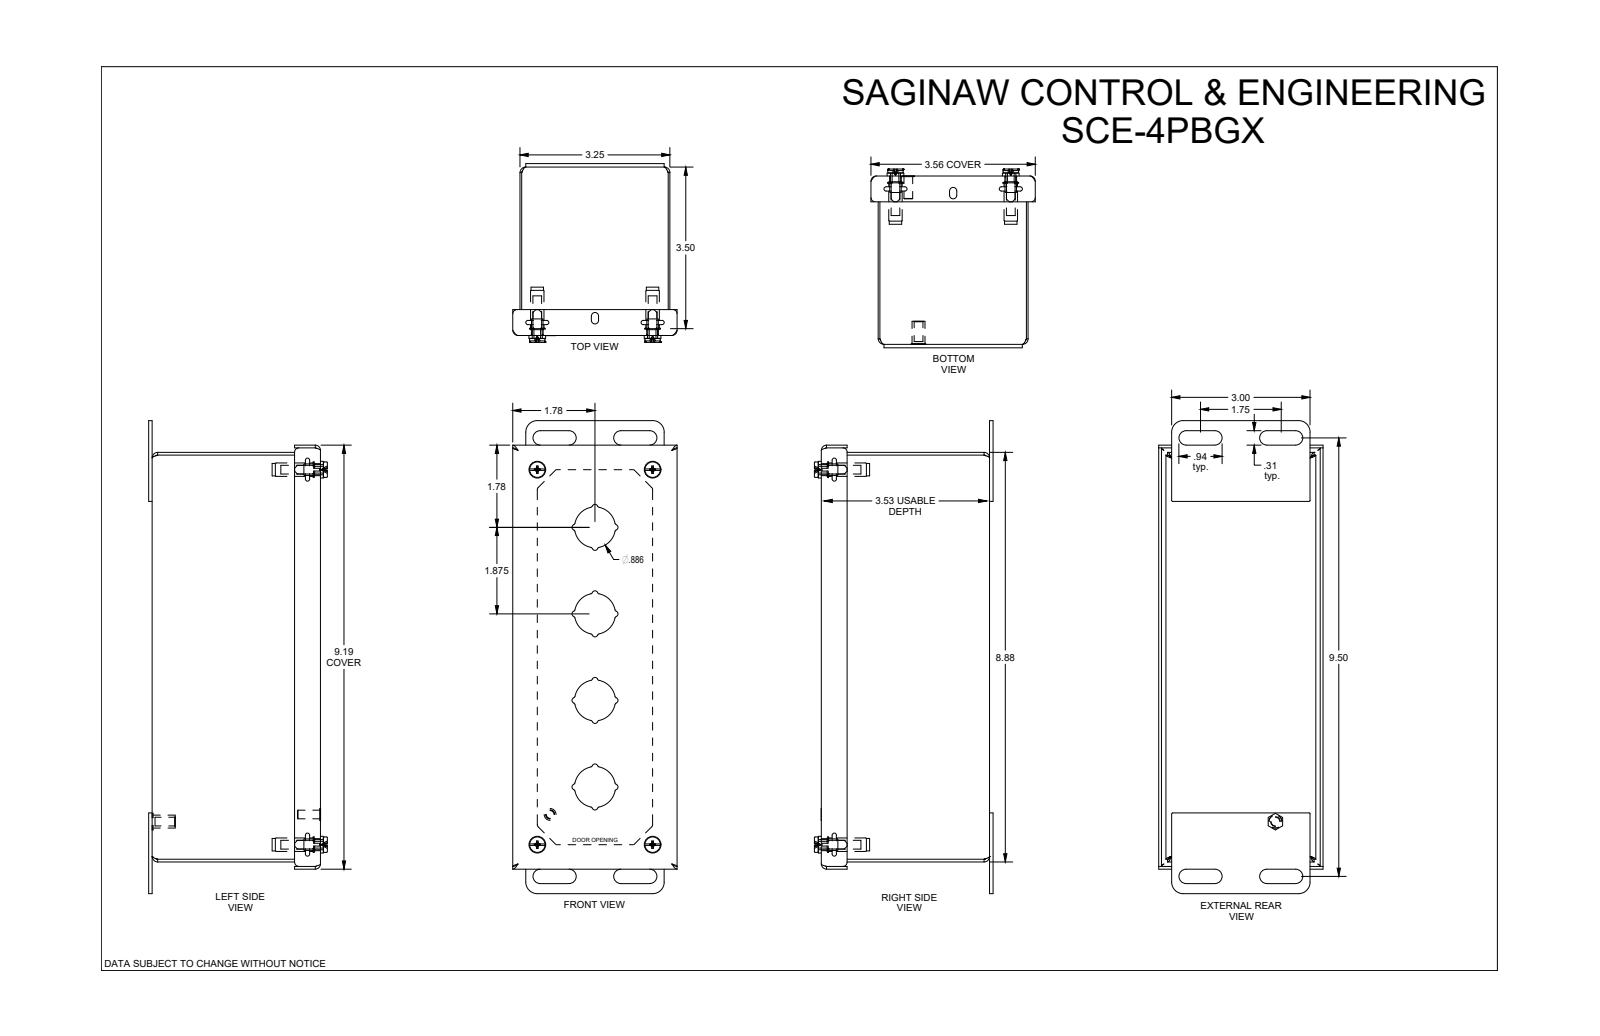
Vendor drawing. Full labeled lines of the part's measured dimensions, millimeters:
Part name (STEP PRODUCT): SCE-4PBGX
STEP written by: SolidWorks 2021 (AUTOMOTIVE_DESIGN)
Units: millimetres
Bodies: 3 solids, 480 faces (153 planar, 243 cylindrical, 84 other)
Overall size (bounding box): 260.4 × 96.2 × 90.5
Volume: 180 400 mm³ · Surface area: 228 900 mm²
Round holes (diameter × count): ⌀4.8 ×5, ⌀5.6 ×4, ⌀6.4 ×4, ⌀6.8 ×4, ⌀8.1 ×4
Round bosses / shafts (diameter × count): ⌀9.2 ×4, ⌀8.6 ×4, ⌀7.4 ×4, ⌀6.9 ×4, ⌀6.6 ×4, ⌀7.1 ×1, ⌀6.5 ×1, ⌀4.8 ×1
Partial cylindrical surfaces — rounded edges, fillets, slot ends (radius × count): R1 ×32, R1.5 ×20, R1.6 ×16, R0.4 ×8, R2.9 ×8, R4 ×8, R6.2 ×8, R0.5 ×4
Main face-to-face distances: 1.5, 81, 91.1, 82.6, 79.5, 89.6, 92.7, 4, 85, 87.4
Hole centre spacings: 206.4, 215.9, 63.5, 206.4, 215.9, 63.5, 63.5, 194.1
